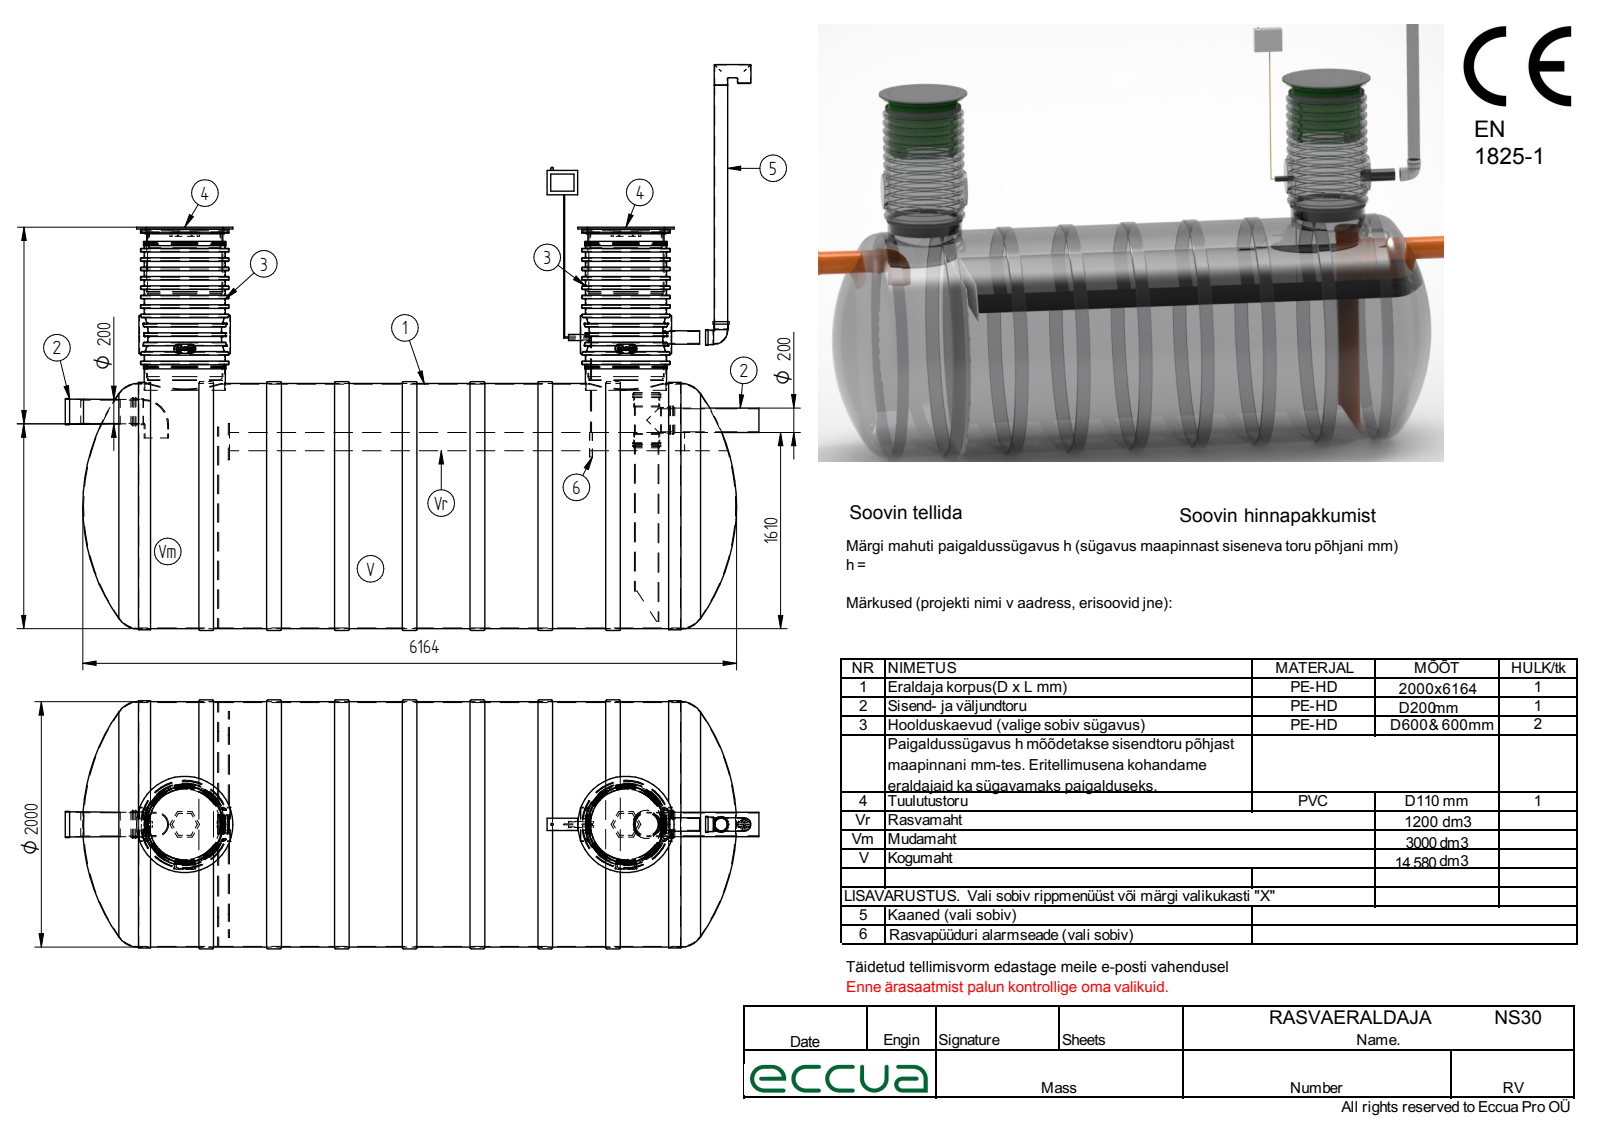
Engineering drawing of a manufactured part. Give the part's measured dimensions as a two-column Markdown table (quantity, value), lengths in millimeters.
| quantity | value |
| --- | --- |
| part name | Rasvaeraldaja NS30; 2381.003; rasvaeraldaja NS30_silinder; 2000 Ribi (+8 more) |
| STEP written by | Solid Edge (AUTOMOTIVE_DESIGN) |
| units | millimeters |
| bodies | 50 solids, 1250 faces (485 planar, 388 cylindrical, 377 other) |
| overall size | 6559 × 4106.27 × 2618.53 |
| volume | 346 900 000 mm³ |
| surface area | 236 000 000 mm² |
| round holes (diameter × count) | 10 × 31, 103.2 × 3, 200 × 3, 6 × 2, 100 × 2, 188 × 2, 220 × 2, 595 × 2, 600 × 2, 609 × 2, 615 × 2, 630 × 2 |
| round bosses / shafts (diameter × count) | 110 × 4, 212 × 3, 8.5 × 3, 790 × 2, 725 × 2, 678.5 × 2, 665 × 2, 650 × 2 |
| partial cylindrical surfaces (radius × count) | 3 × 8, 5 × 8, 30 × 8, 35 × 8, 135 × 4, 140 × 4, 289.9 × 2, 130 × 1 |
| main face-to-face distances | 150, 8, 5, 45, 195, 10, 15, 88, 1126, 1854 |
| hole center spacings | 40, 49.88, 62.55, 17.8, 72.08, 78, 26.75, 34.71 |
